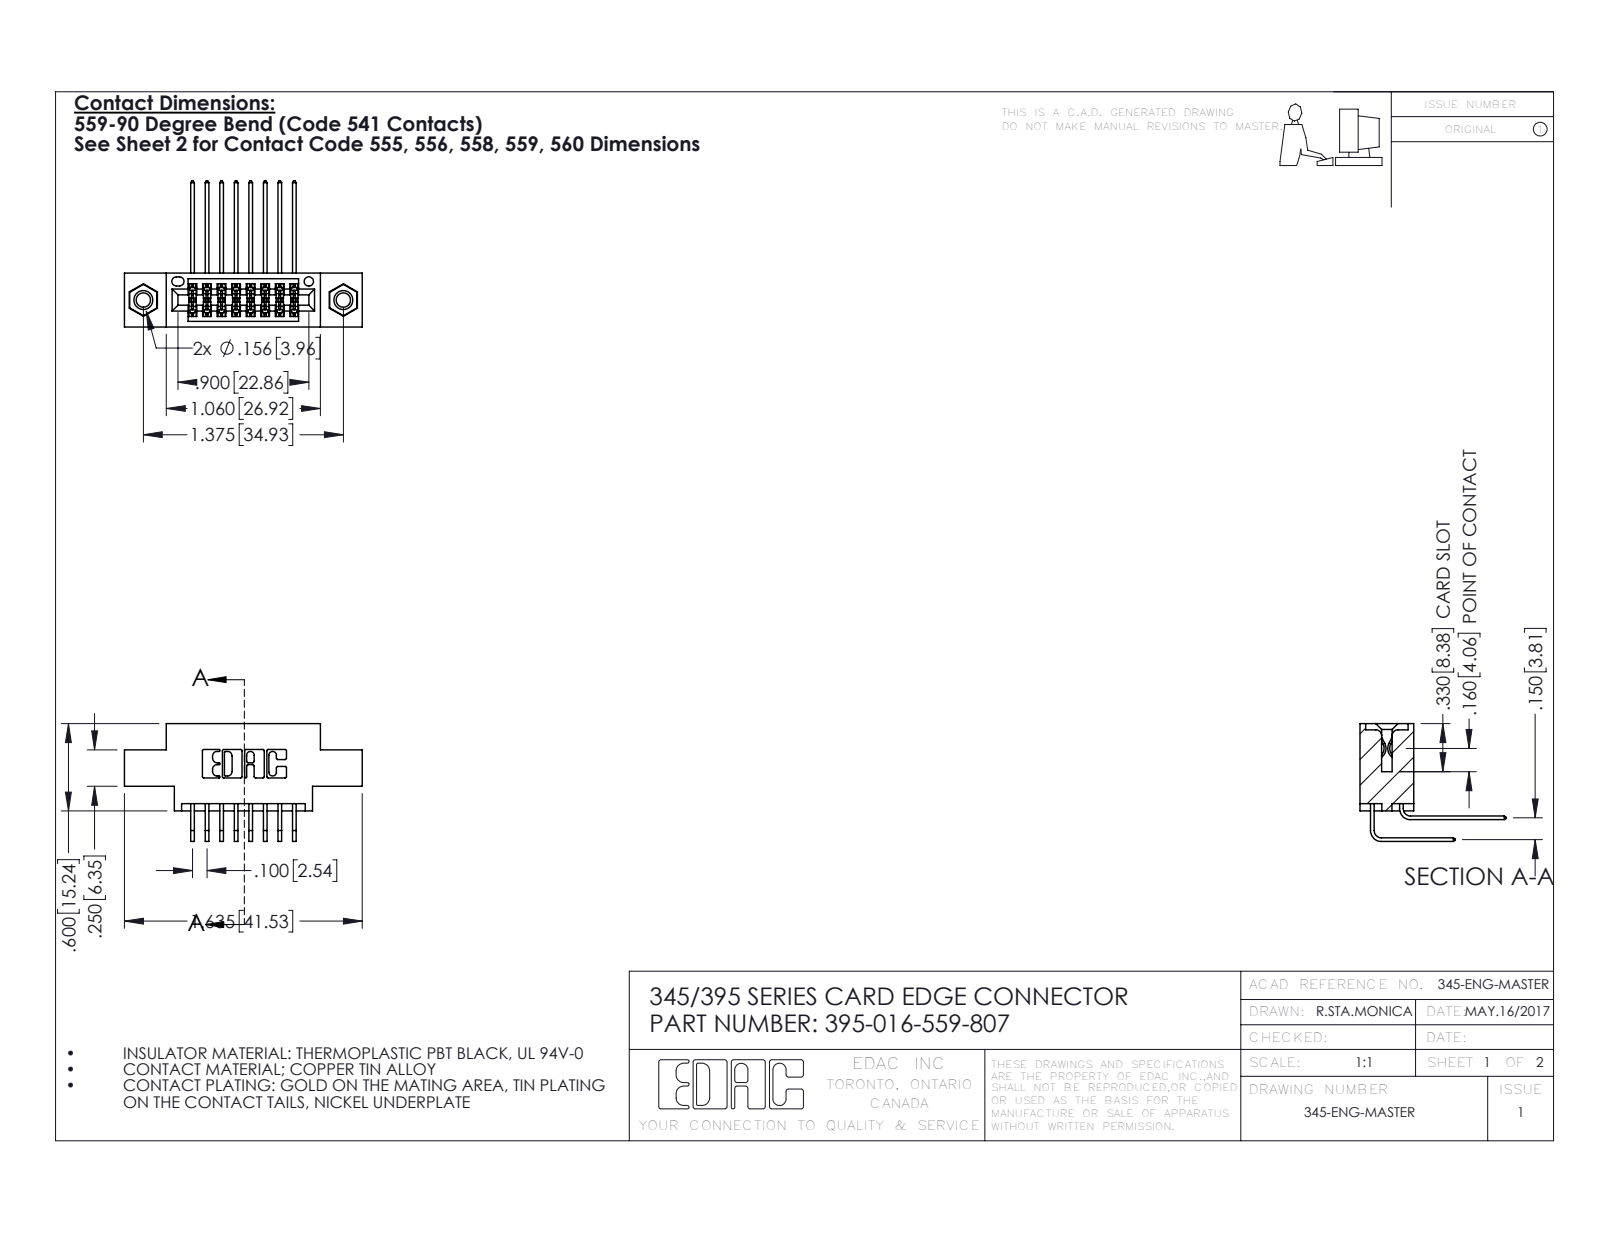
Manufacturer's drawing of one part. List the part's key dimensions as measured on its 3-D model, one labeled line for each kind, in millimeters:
Part name (STEP PRODUCT): 345-250-001_345-250-005-103; 345-292-001_558 559 Tail - 1; 345-292-001_559 Tail - 2; 395-016-559-807 (+1 more)
STEP written by: SolidWorks 2016 (CONFIG_CONTROL_DESIGN)
Units: millimetres
Bodies: 19 solids, 1022 faces (676 planar, 330 cylindrical, 16 other)
Overall size (bounding box): 41.5 × 25.5 × 20.5
Volume: 3 690 mm³ · Surface area: 5 392 mm²
Round holes (diameter × count): ⌀2.5 ×2, ⌀3.2 ×2, ⌀4 ×2, ⌀1.6 ×1
Round bosses / shafts (diameter × count): ⌀3.9 ×2
Partial cylindrical surfaces — rounded edges, fillets, slot ends (radius × count): R0.2 ×25, R0.3 ×22, R0.2 ×6, R0.8 ×6, R0.7 ×3, R0.4 ×2, R0.5 ×2, R0.6 ×2
Main face-to-face distances: 5.1, 9.4, 1.8, 7.6, 2.5, 3.8, 2.5, 6.9, 0.6, 4.4
Hole centre spacings: 6.9, 29.1, 34.9
